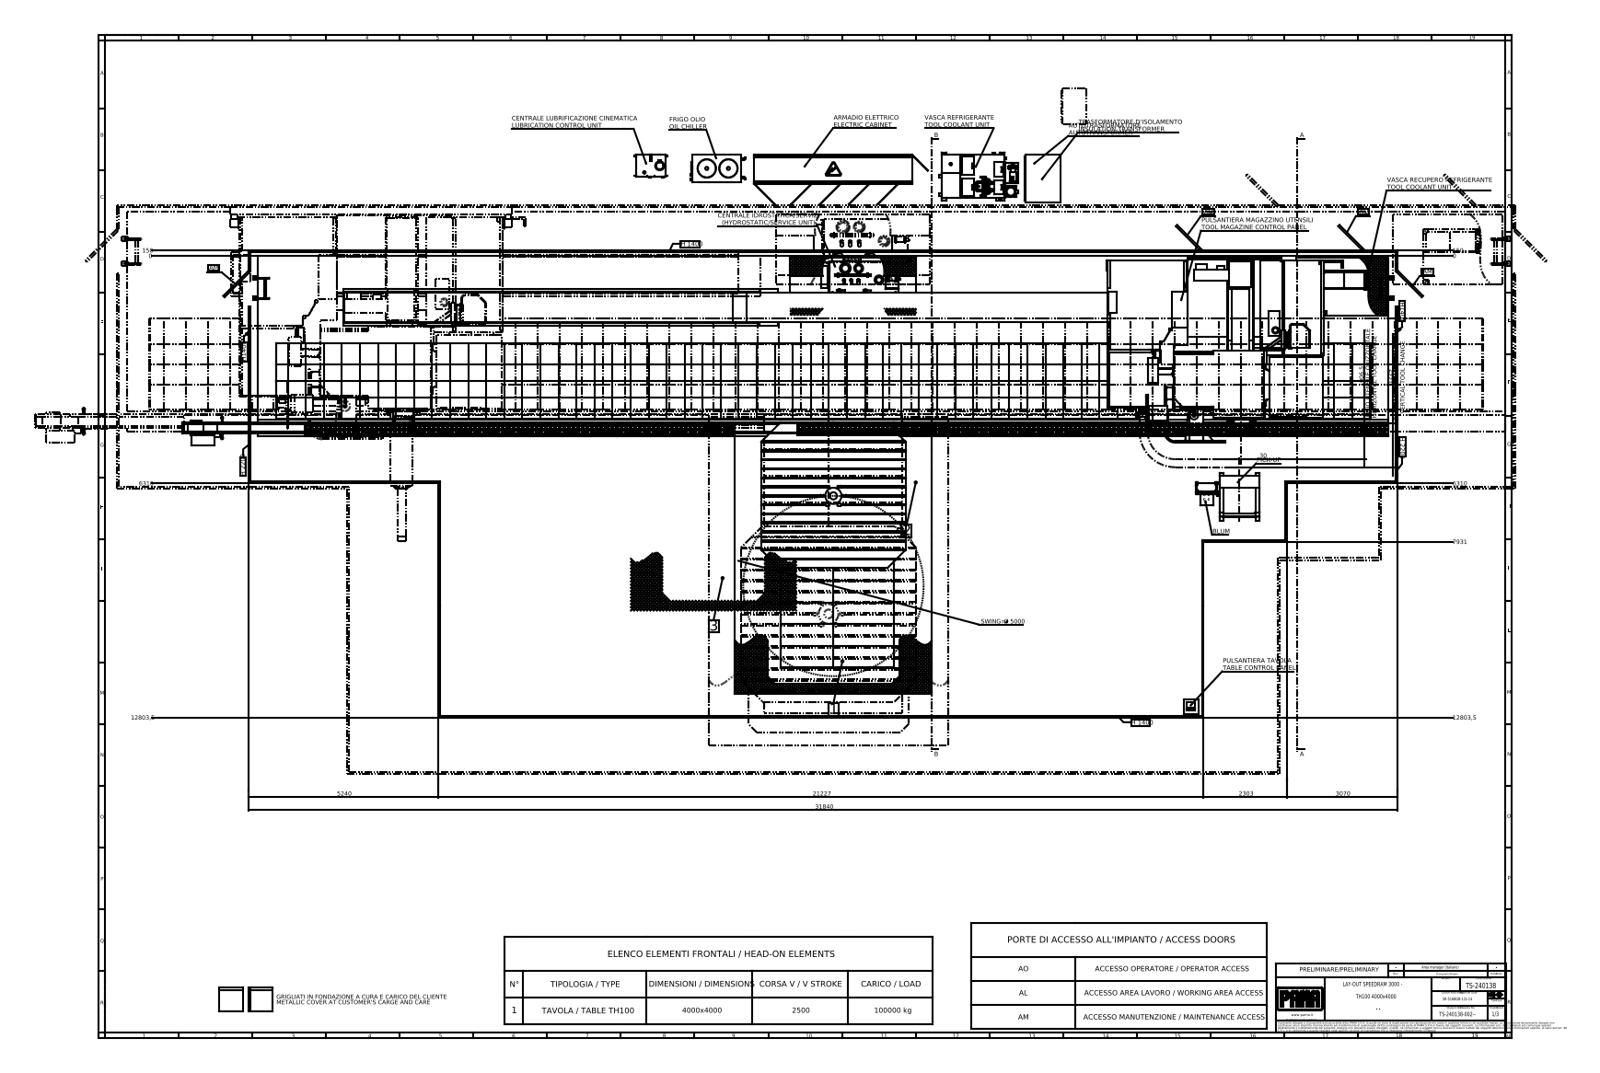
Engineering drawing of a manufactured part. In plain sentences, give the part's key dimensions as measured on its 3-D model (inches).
The part is named "S001560_3 (2+1) POSTI; S003258_ISO 50 - RIPOSO; S003390; S001813_4000x4000 (PASSO CAVA = 250) SM. 500x500 (+8 more)". Its 3-D file was written by "SolidWorks 2023 (AUTOMOTIVE_DESIGN)". It is 464 solids with 8460 faces: 5620 planar, 2102 cylindrical and 738 other. Overall it measures 1391.339 by 733.264 by 431.535 inches. Its volume is 68 530 000 cubic inches and its surface area 5 301 000 square inches. Round holes: 240 of diameter 1.378, 63 of diameter 2.74, 18 of diameter 1.465, 17 of diameter 0.197, 9 of diameter 0.276, 9 of diameter 1.181, 8 of diameter 0.512, 8 of diameter 0.551, 7 of diameter 0.433, 6 of diameter 0.315, 4 of diameter 0.26, 4 of diameter 0.492. Round bosses or shafts: 18 of diameter 1.669, 15 of diameter 0.787, 11 of diameter 1.575, 10 of diameter 0.354, 8 of diameter 2.165, 7 of diameter 2.61, 6 of diameter 2.362, 6 of diameter 1.378. Partial cylindrical surfaces (rounded edges, fillets, slot ends): 156 of radius 0.197, 53 of radius 0.591, 52 of radius 0.315, 27 of radius 0.157, 26 of radius 0.236, 26 of radius 1.378, 24 of radius 0.394, 21 of radius 0.118. The main face-to-face distances are 78.74, 1.969, 29.646, 49.094, 5.906, 0.394, 730.453, 508.012, 306.929, 423.524. The hole center spacings are 10.753, 19.685, 48.644, 29.843, 56.047, 39.37, 5.118, 10.236.
